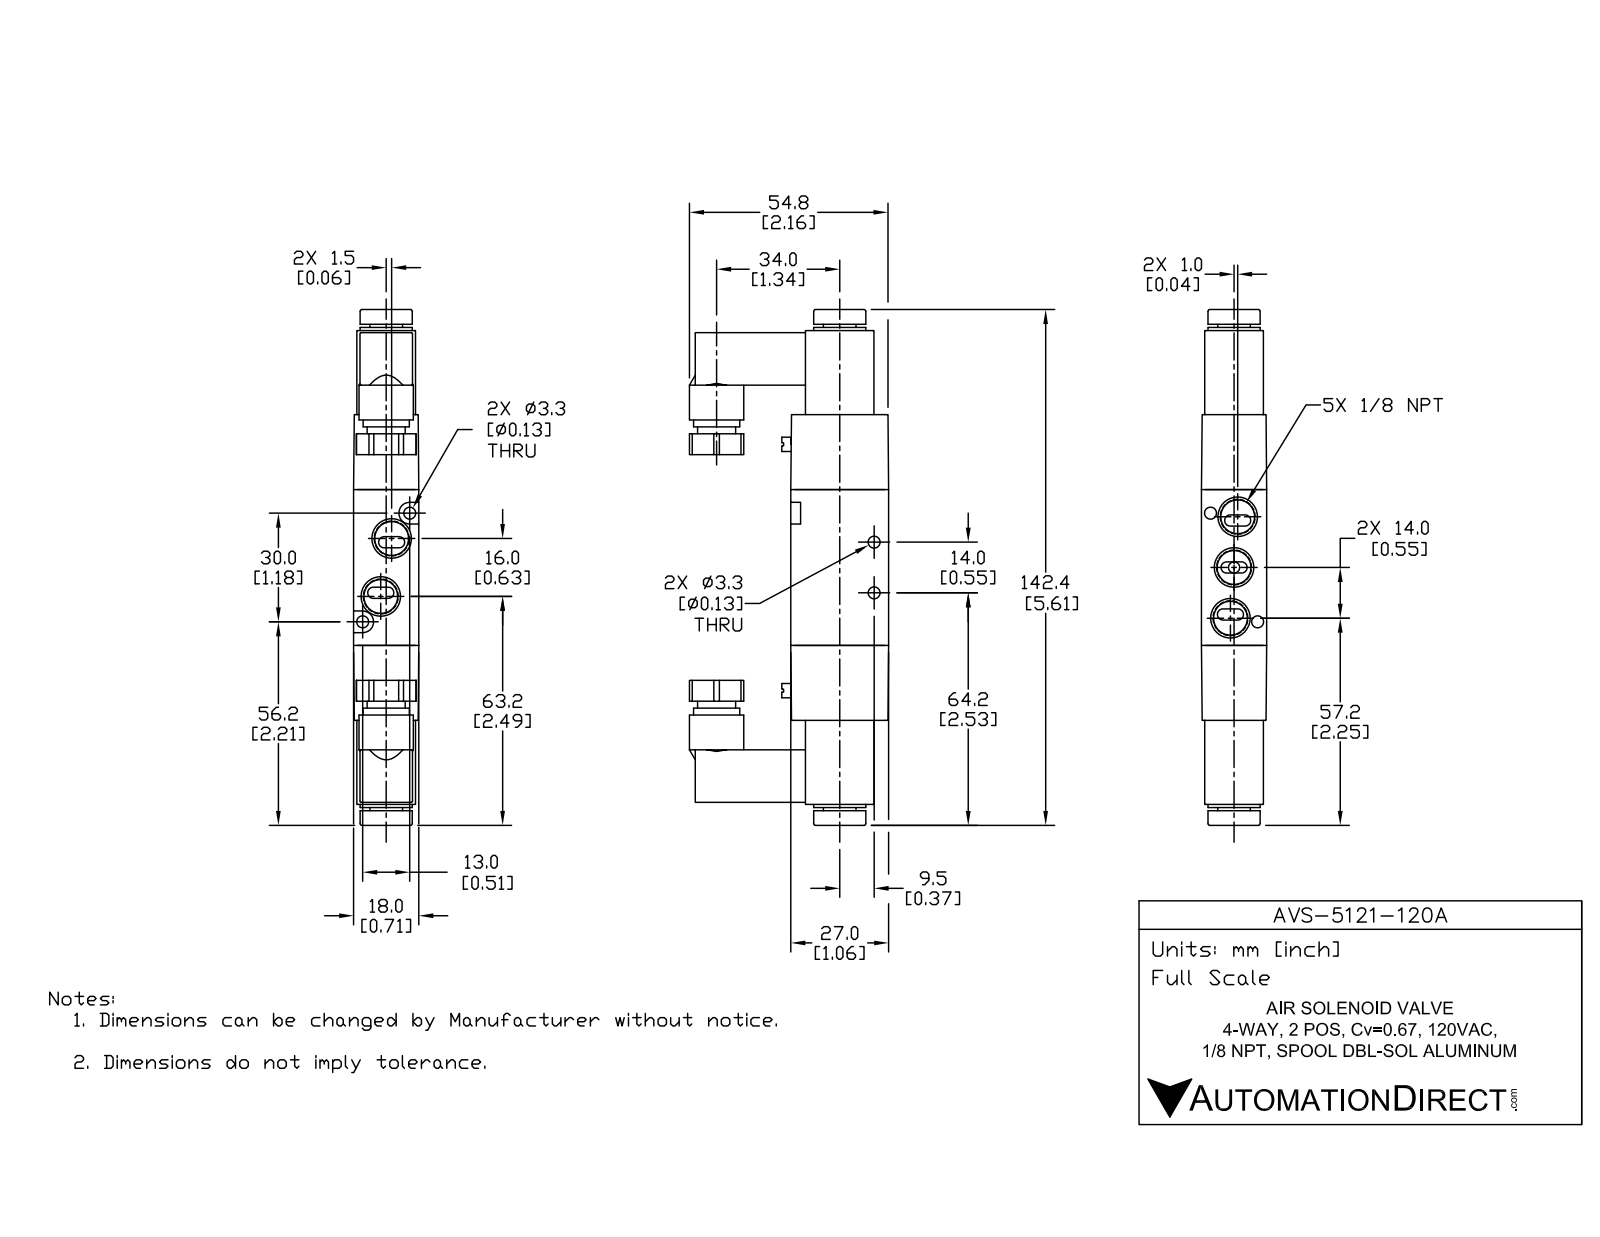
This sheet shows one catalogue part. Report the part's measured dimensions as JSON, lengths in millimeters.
{"part_name": "AVS-5121-120A", "step_written_by": "SolidWorks 2015 (CONFIG_CONTROL_DESIGN)", "units": "millimeters", "bodies": {"solids": 5, "faces": 254, "planar": 131, "cylindrical": 91, "other": 32}, "overall_size": [142.6, 55, 18], "volume_mm3": 69237, "surface_area_mm2": 23595, "round_holes": [[8.43, 5], [3.3, 3], [3.2, 1], [9.3, 1]], "round_bosses_or_shafts": [[6.8, 2], [15, 1], [14.4, 1], [12.8, 1], [10.5, 1], [9, 1]], "partial_cylinders_radius": [[1.54, 10], [0.3, 8], [0.5, 8], [1, 8], [3, 2]], "face_to_face_distances": [1.75, 16.25, 0.81, 17.57, 14.5, 18, 18.38, 43, 23.52, 3.86], "hole_center_spacings": [7.57, 14.04, 16.35, 29.52, 6.25, 6.82, 8.04, 8.19]}
